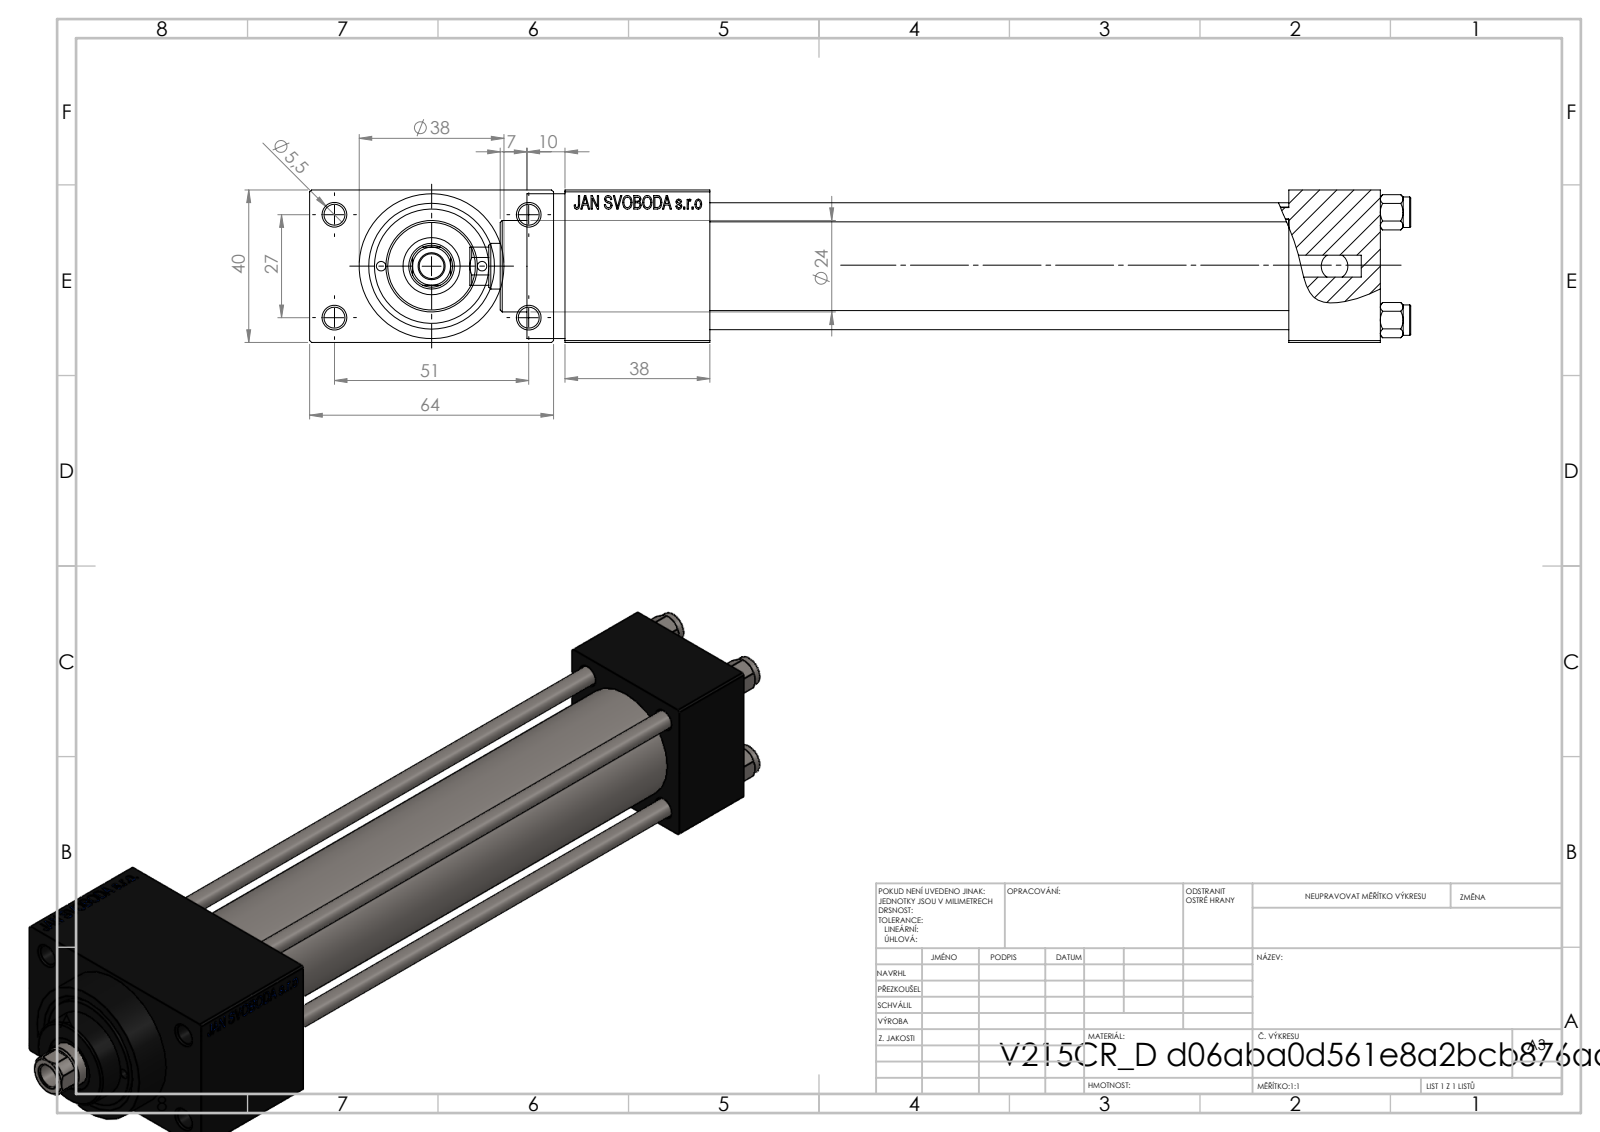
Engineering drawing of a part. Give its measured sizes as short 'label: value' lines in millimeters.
name: V215_VC_A; V215CR_D_TYCINKA; V215CR_D_Body; NUT_M5_D (+1 more)
written by: SolidWorks 2019 (CONFIG_CONTROL_DESIGN)
unit: mm
bodies: 11 solids, 1110 faces (498 planar, 92 cylindrical, 520 other)
size: 247 × 64 × 40
volume: 221 355 mm³; area: 91 187 mm²
holes: 4× ⌀5, 4× ⌀5.5, 3× ⌀20, 2× ⌀2.5, 2× ⌀7, 2× ⌀13.16, 1× ⌀6.5, 1× ⌀12, 1× ⌀15, 1× ⌀25, 1× ⌀30
bosses: 4× ⌀8, 1× ⌀38, 1× ⌀31, 1× ⌀24
rounds: 1× R5.5
face distances: 40, 12, 152, 24, 176, 52, 38, 214, 190, 64
hole spacings: 11.37, 14.18, 18.23, 20.01, 28.3, 28.85, 29.89, 30.84
